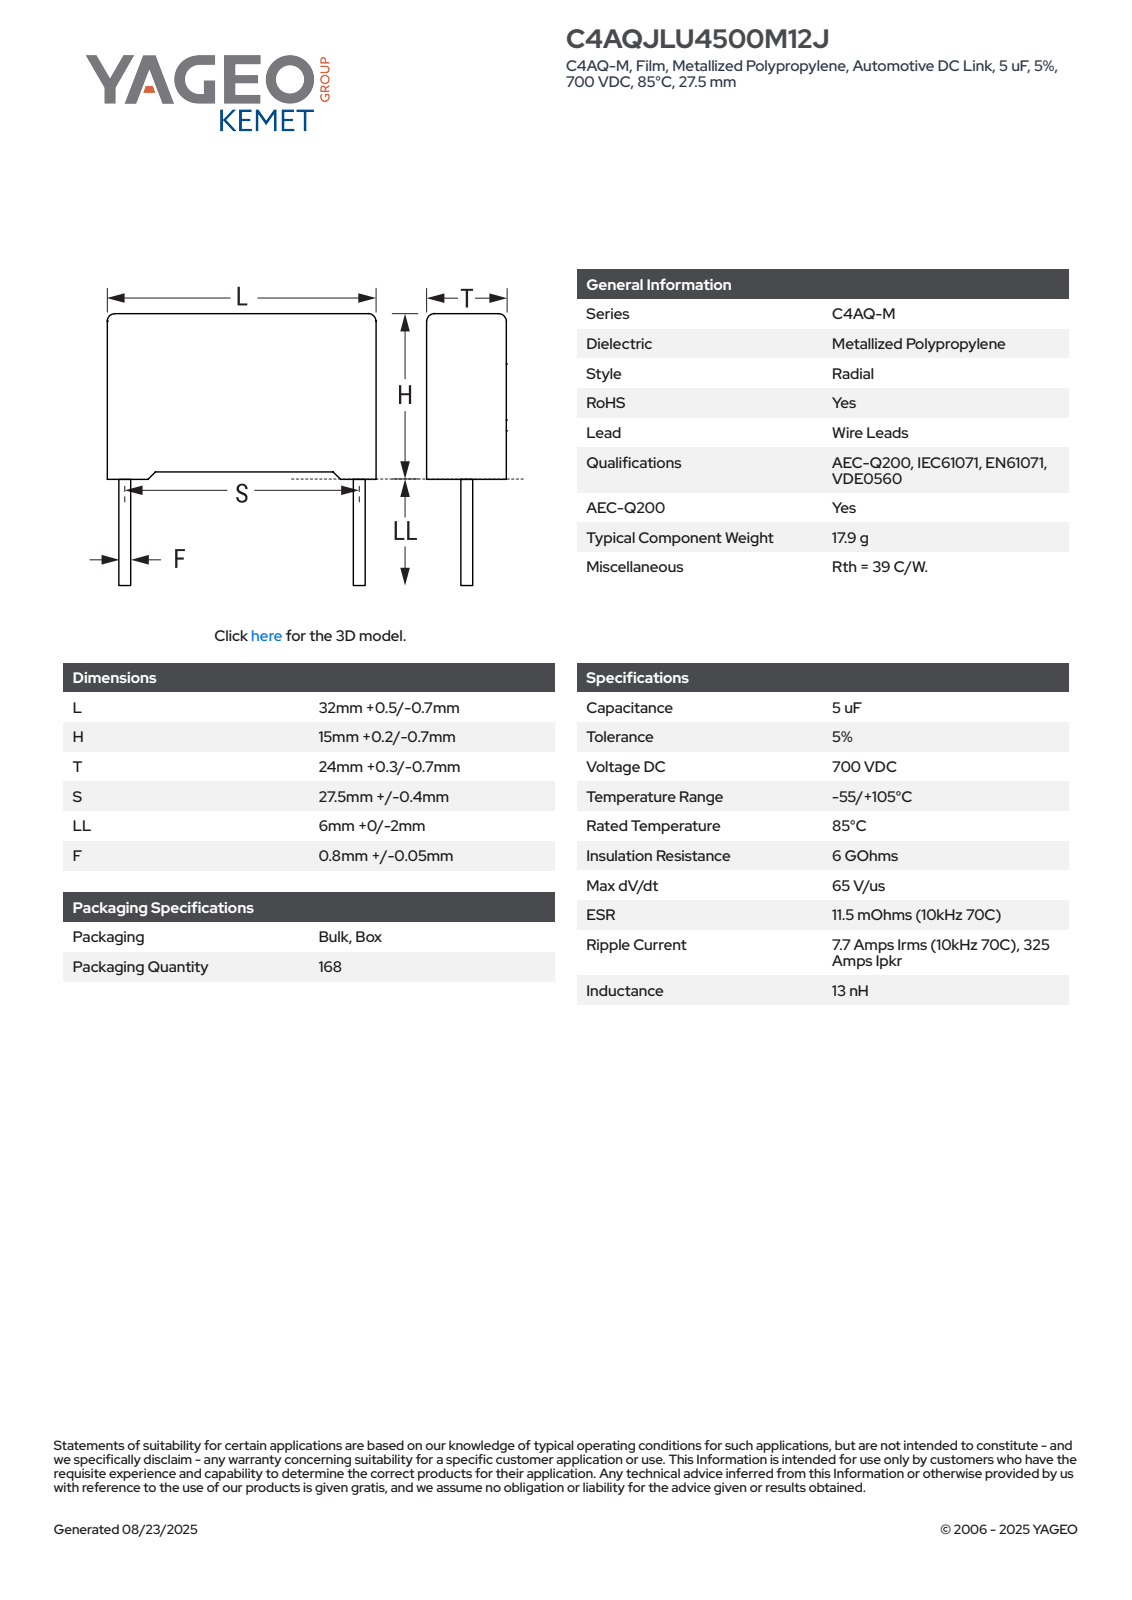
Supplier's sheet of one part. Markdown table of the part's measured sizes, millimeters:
| quantity | value |
| --- | --- |
| part name | CFR_RB2CFP_32X15X24_L32.5H15.2T24.3S27.5LL6F0.85 |
| STEP written by | SolidWorks 2014 (AUTOMOTIVE_DESIGN) |
| units | millimeters |
| bodies | 4 solids, 85 faces (77 planar, 8 cylindrical, 0 other) |
| overall size | 32.5 × 24.3 × 21.2 |
| volume | 11 476 mm³ |
| surface area | 3 427 mm² |
| round bosses / shafts (diameter × count) | 0.85 × 2 |
| partial cylindrical surfaces (radius × count) | 0.5 × 4 |
| main face-to-face distances | 14.45, 24.3, 32.5, 0.75, 15.2, 1.08, 0.52, 14.68, 31.42, 23.22 |
